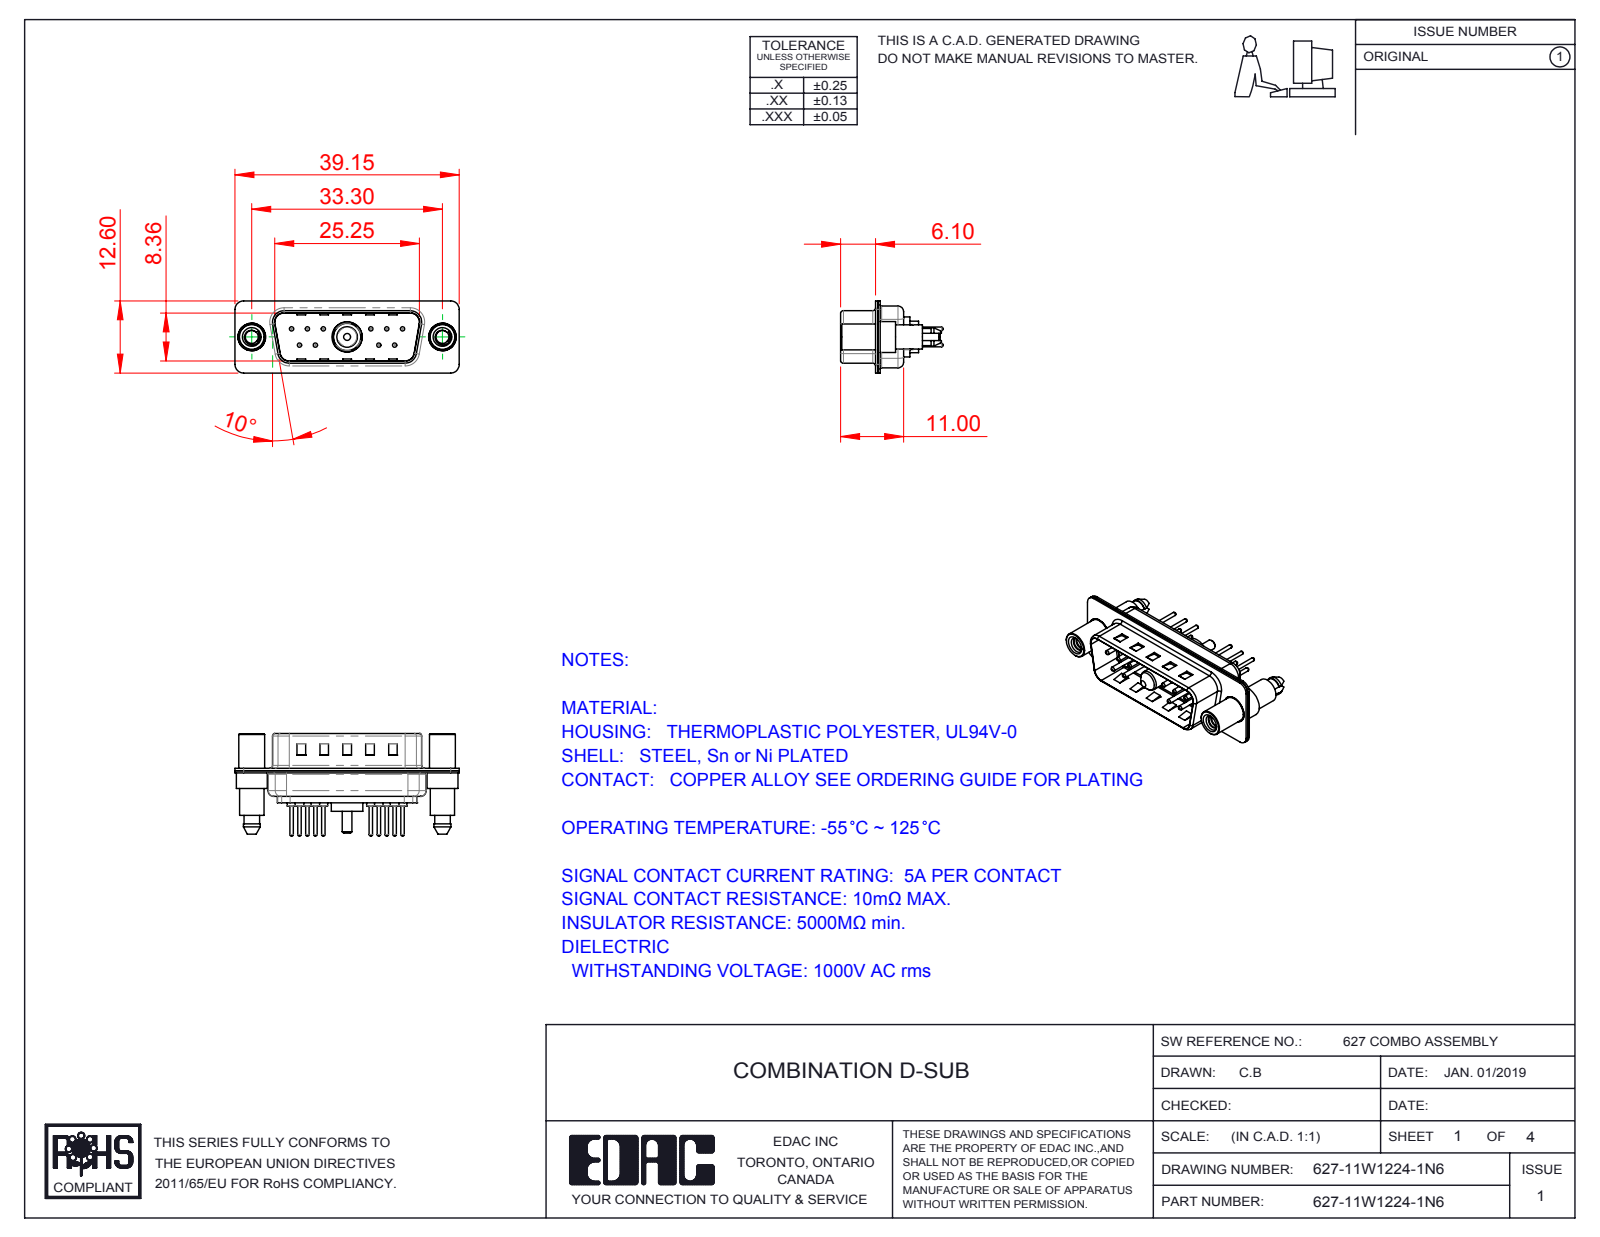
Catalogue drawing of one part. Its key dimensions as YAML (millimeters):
part_name: "627Combo Contact Row 2_24; 627Combo Threaded Standoff and Boardlock_6; 627-11W1224-1N6; Power Pin_10A S (+4 more)"
step_written_by: "SolidWorks 2016 (CONFIG_CONTROL_DESIGN)"
units: millimeters
bodies: {solids: 17, faces: 815, planar: 246, cylindrical: 324, other: 245}
overall_size: [39.15, 17.9, 12.6]
volume: 2235
surface_area: 5245
round_holes:
  - {diameter: 0.75, count: 10}
  - {diameter: 1.6, count: 10}
  - {diameter: 2, count: 10}
  - {diameter: 2.26, count: 2}
  - {diameter: 4, count: 2}
  - {diameter: 4.8, count: 2}
  - {diameter: 4.85, count: 1}
  - {diameter: 5.3, count: 1}
round_bosses_or_shafts:
  - {diameter: 1.5, count: 10}
  - {diameter: 0.6, count: 10}
  - {diameter: 5.4, count: 2}
  - {diameter: 4.9, count: 2}
  - {diameter: 4.5, count: 2}
  - {diameter: 4.25, count: 2}
  - {diameter: 5.5, count: 1}
  - {diameter: 5.2, count: 1}
partial_cylinders:
  - {radius: 1.5, count: 22}
  - {radius: 2, count: 12}
  - {radius: 1.6, count: 10}
  - {radius: 0.5, count: 8}
  - {radius: 1, count: 7}
  - {radius: 0.25, count: 4}
  - {radius: 0.6, count: 4}
  - {radius: 0.65, count: 4}
face_to_face_distances: [0.4, 0.82, 9.58, 0.8, 8.76, 1.5, 5.2, 5.6, 6, 1.4]
hole_center_spacings: [3.16, 2.77, 13.85, 11.08, 16.62, 5.03, 5.04, 5.54]
